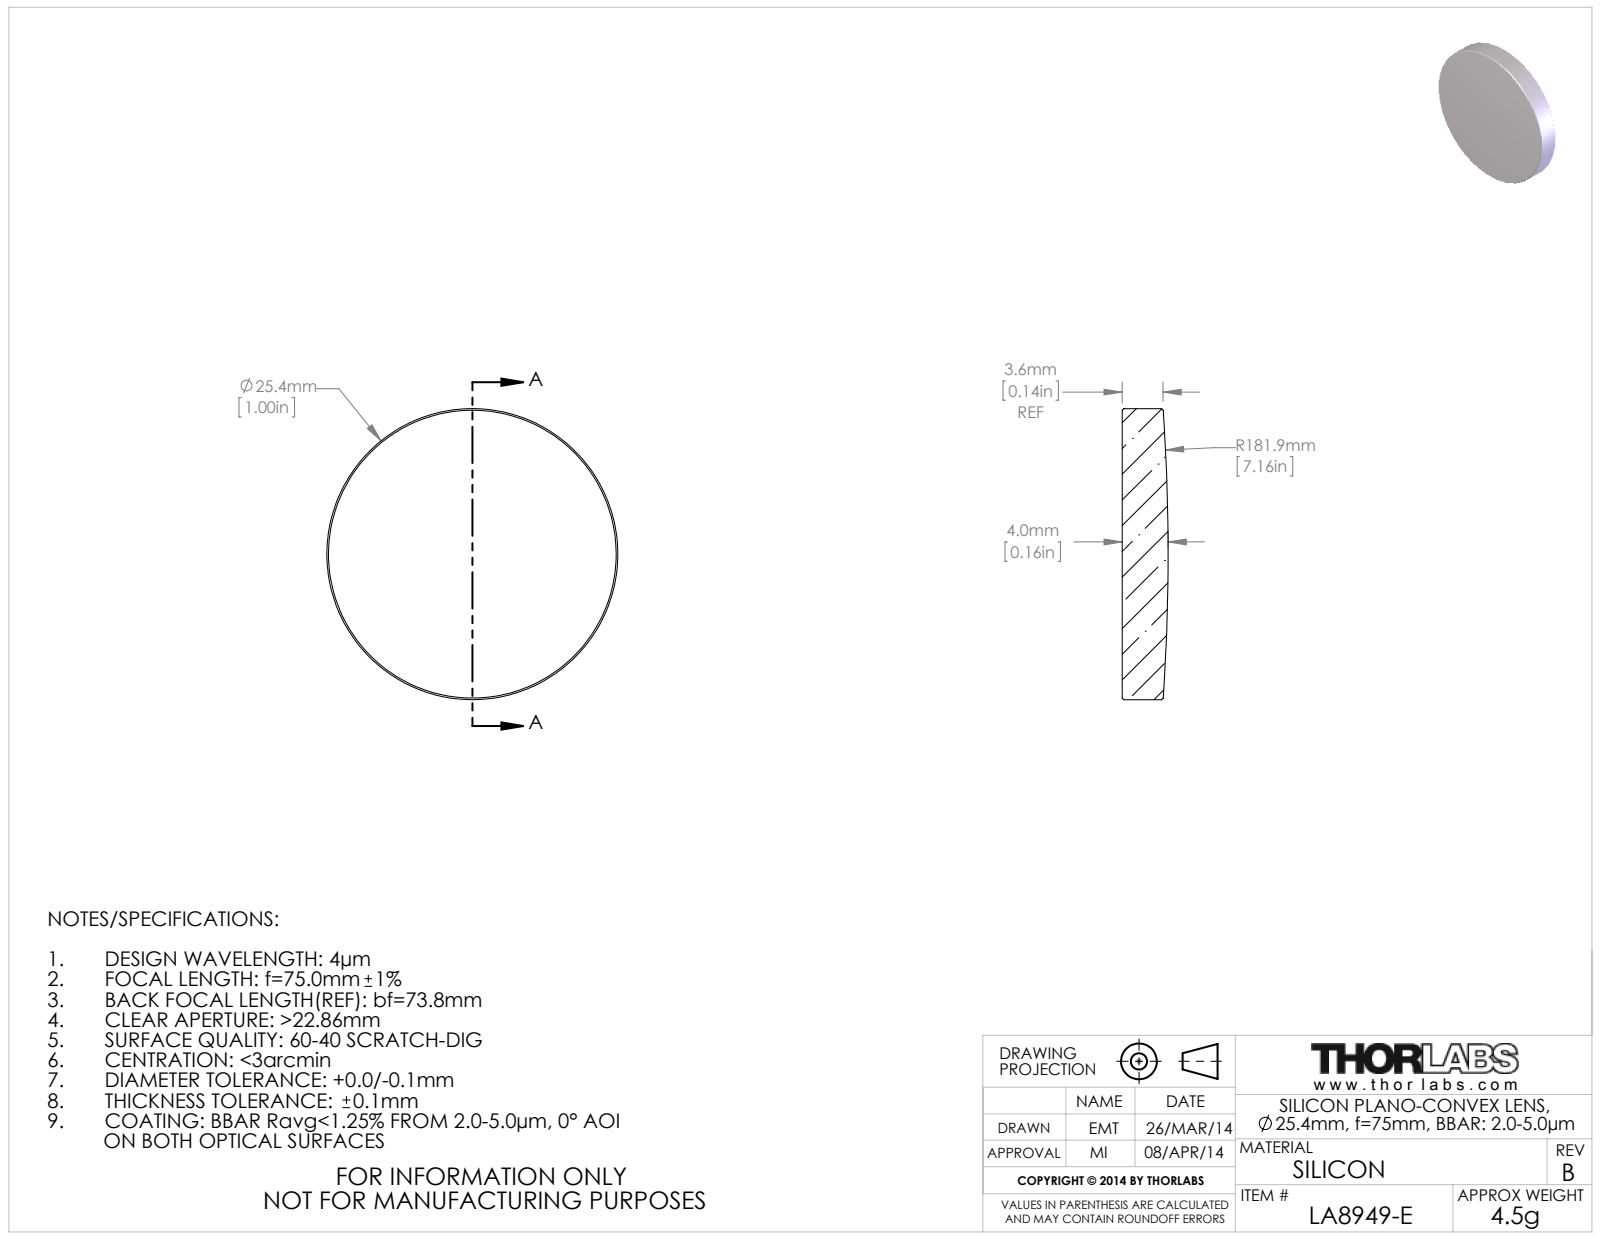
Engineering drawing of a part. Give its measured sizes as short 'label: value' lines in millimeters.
name: 20118-E0W
written by: SolidWorks 2014 (CONFIG_CONTROL_DESIGN)
unit: mm
bodies: 1 solid, 9 faces (1 planar, 2 cylindrical, 6 other)
size: 25.4 × 25.4 × 4
volume: 1 913 mm³; area: 1 285 mm²
bosses: 1× ⌀25.4
